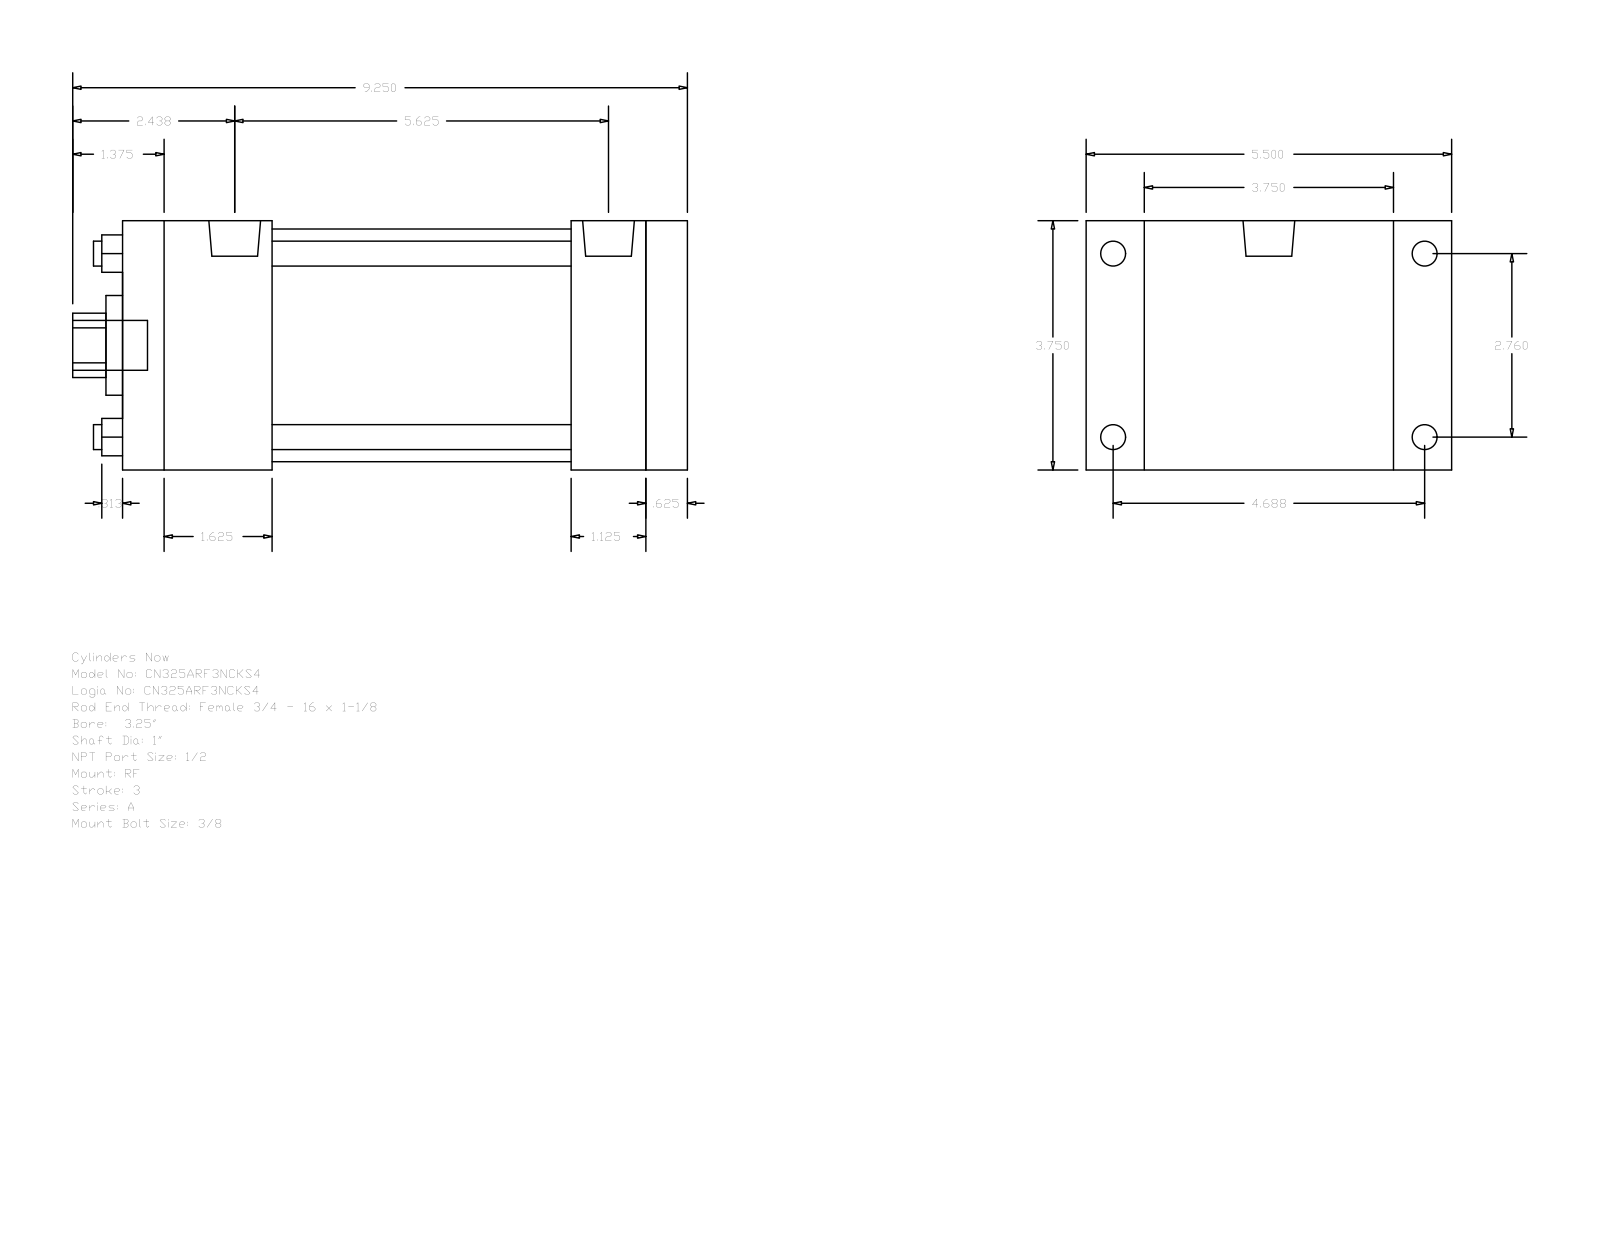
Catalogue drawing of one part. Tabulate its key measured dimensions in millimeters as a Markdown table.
| quantity | value |
| --- | --- |
| part name | A_RF__0325_1 |
| STEP written by | GSSL Pune (CONFIG_CONTROL_DESIGN) |
| units | millimeters |
| bodies | 0 solids, 92 faces (64 planar, 28 cylindrical, 0 other) |
| overall size | 234.95 × 139.7 × 95.25 |
| round holes (diameter × count) | 9.53 × 4, 25.4 × 1, 38.1 × 1, 88.9 × 1 |
| round bosses / shafts (diameter × count) | 9.53 × 4, 8.73 × 4, 19.77 × 2, 19.05 × 1 |
| partial cylindrical surfaces (radius × count) | 12.29 × 1 |
| main face-to-face distances | 95.24, 215.9, 200.02, 15.88, 22.23, 117.47, 28.57, 171.45, 44.45, 57.15 |
| hole center spacings | 49.57, 70.1, 99.14 |
